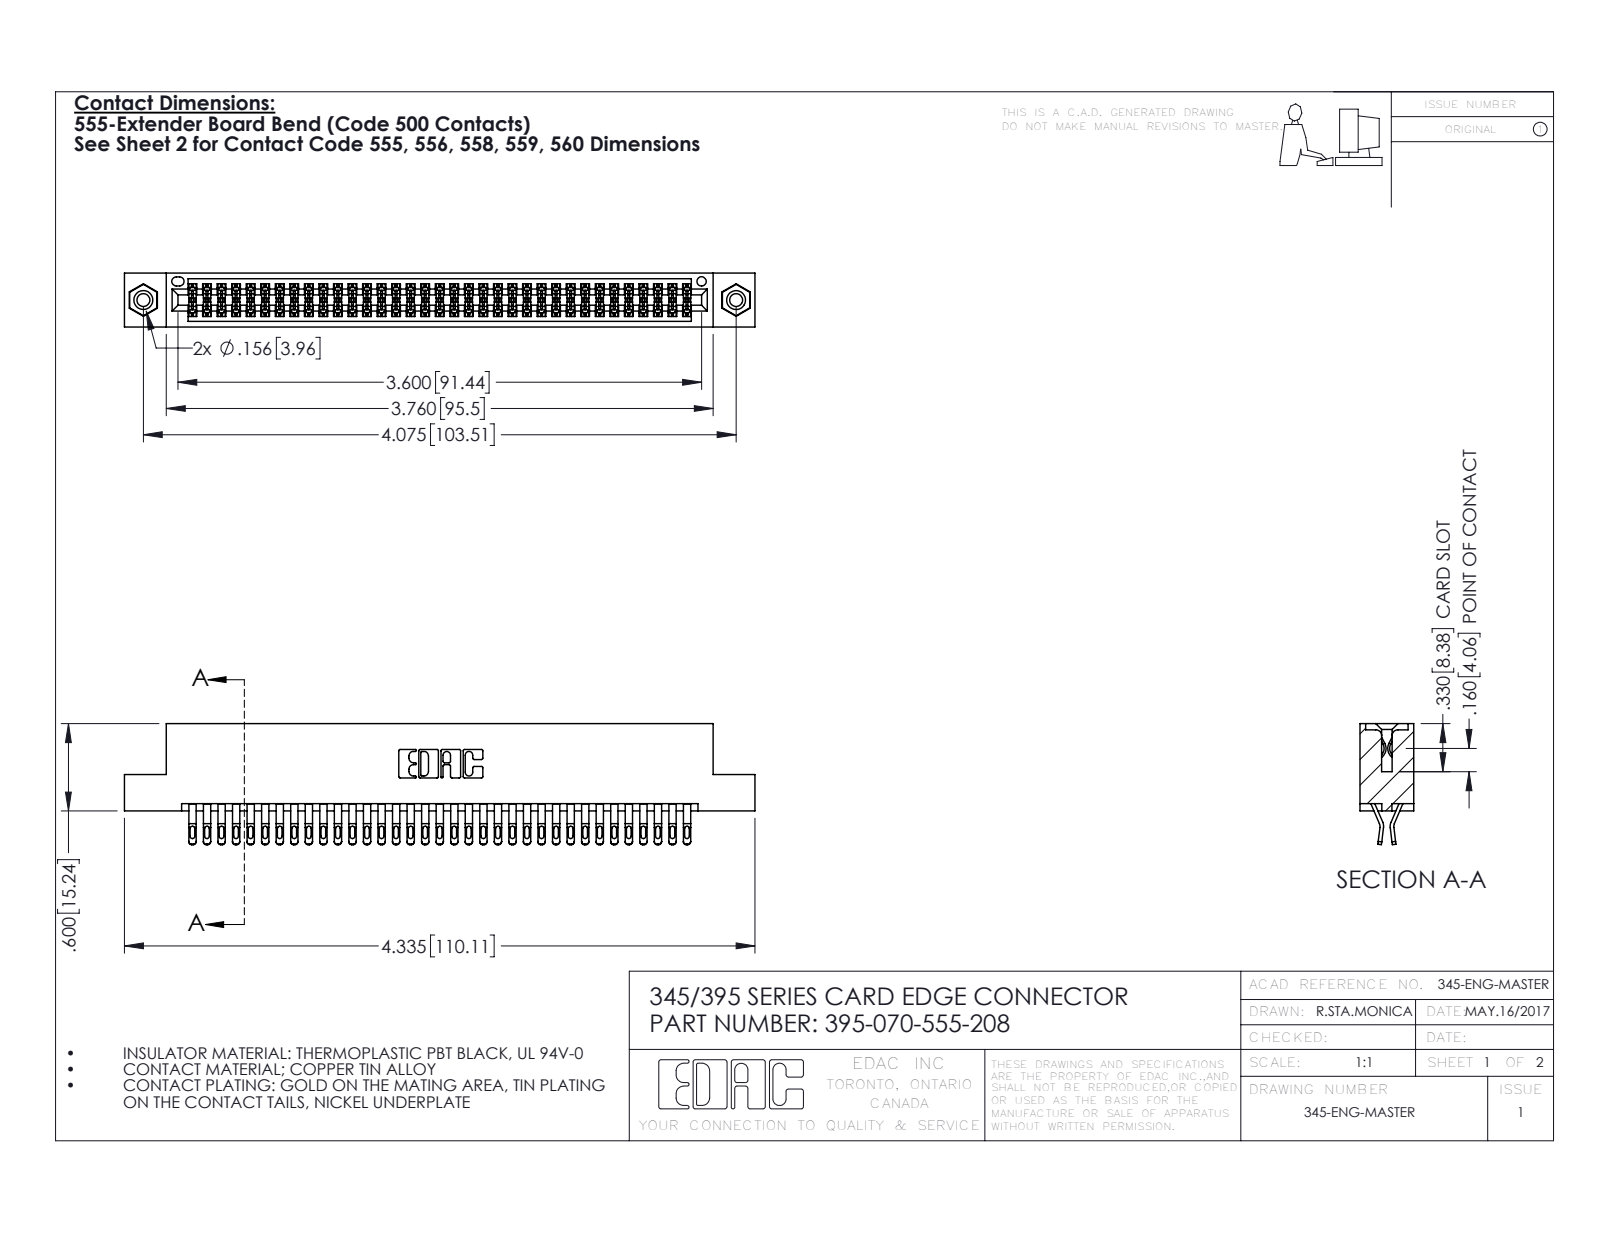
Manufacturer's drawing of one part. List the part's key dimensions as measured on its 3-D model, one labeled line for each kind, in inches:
Part name (STEP PRODUCT): 345-292-001_555 Tail; 345-250-001_345-250-003-102; 395-070-555-208; 345 Part_Flush Mounting Lugs - 0.156 Dia-TI
STEP written by: SolidWorks 2016 (CONFIG_CONTROL_DESIGN)
Units: inches
Bodies: 73 solids, 4106 faces (2282 planar, 1808 cylindrical, 16 other)
Overall size (bounding box): 4.335 × 0.832 × 0.37
Volume: 0.661 in³ · Surface area: 25.71 in²
Round holes (diameter × count): ⌀0.089 ×2, ⌀0.125 ×2, ⌀0.156 ×2, ⌀0.064 ×1
Round bosses / shafts (diameter × count): ⌀0.155 ×2
Partial cylindrical surfaces — rounded edges, fillets, slot ends (radius × count): R0.016 ×175, R0.02 ×140, R0.006 ×105, R0.01 ×22, R0.007 ×6, R0.031 ×6, R0.026 ×3, R0.01 ×2
Main face-to-face distances: 0.072, 0.298, 0.37, 0.025, 0.2, 0.098, 0.272, 0.225, 0.175, 0.149
Hole centre spacings: 0.27, 3.839, 4.075
